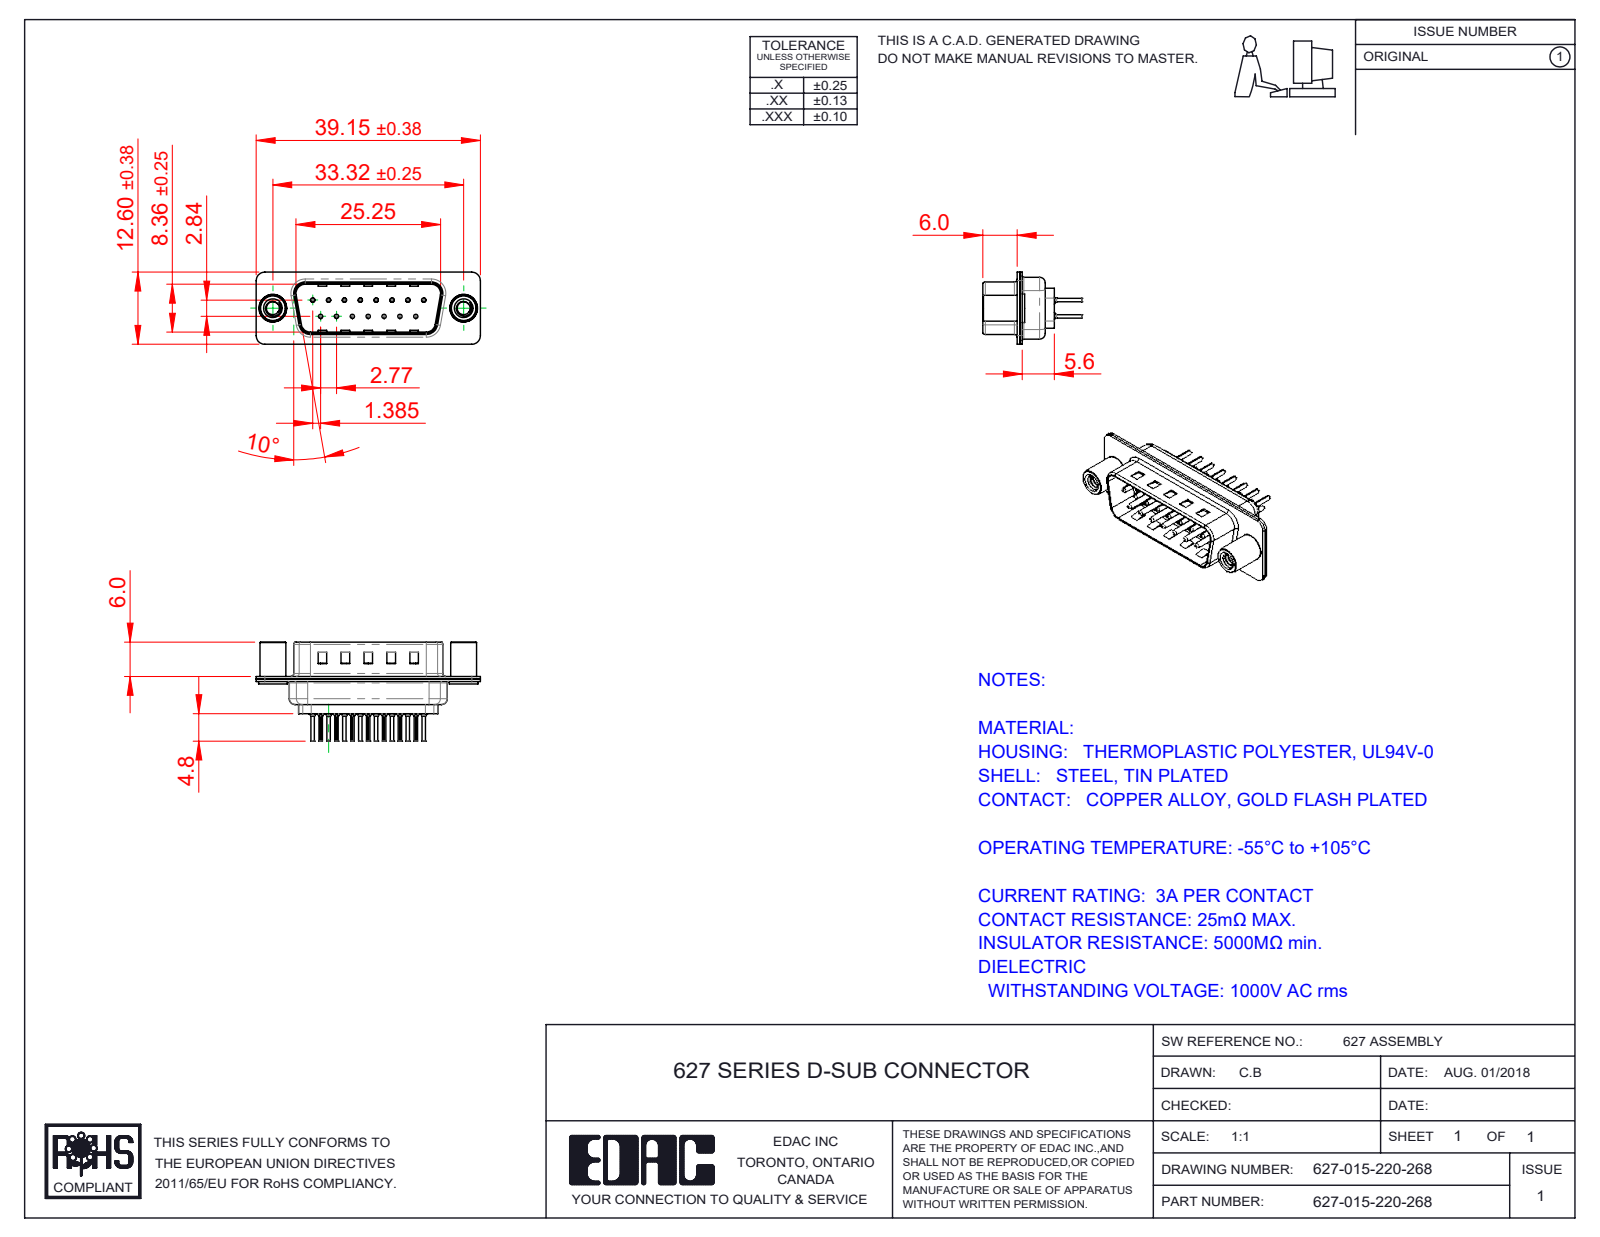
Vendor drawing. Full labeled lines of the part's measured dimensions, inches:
Part name (STEP PRODUCT): 627 Contact Row 2_20L; 627-015-220-268; 627 Contact Row 1_20L; 627 Shell Rear_15 Contacts (+3 more)
STEP written by: SolidWorks 2020 (CONFIG_CONTROL_DESIGN)
Units: inches
Bodies: 20 solids, 1844 faces (501 planar, 716 cylindrical, 627 other)
Overall size (bounding box): 1.541 × 0.681 × 0.496
Volume: 0.116 in³ · Surface area: 8.66 in²
Round holes (diameter × count): ⌀0.008 ×15, ⌀0.014 ×15, ⌀0.043 ×15, ⌀0.063 ×15, ⌀0.089 ×2, ⌀0.157 ×2, ⌀0.189 ×2
Round bosses / shafts (diameter × count): ⌀0.079 ×15, ⌀0.059 ×15, ⌀0.03 ×15, ⌀0.024 ×15, ⌀0.197 ×2, ⌀0.193 ×2, ⌀0.177 ×2
Partial cylindrical surfaces — rounded edges, fillets, slot ends (radius × count): R0.004 ×30, R0.059 ×16, R0.079 ×12, R0.02 ×8, R0.063 ×8, R0.01 ×4, R0.024 ×4, R0.026 ×4
Main face-to-face distances: 0.016, 0.018, 0.035, 0.032, 0.377, 0.345, 0.059, 0.055, 0.256, 0.22
Hole centre spacings: 0.124, 0.109, 0.218, 0.327, 0.436, 0.198, 0.198, 0.294
